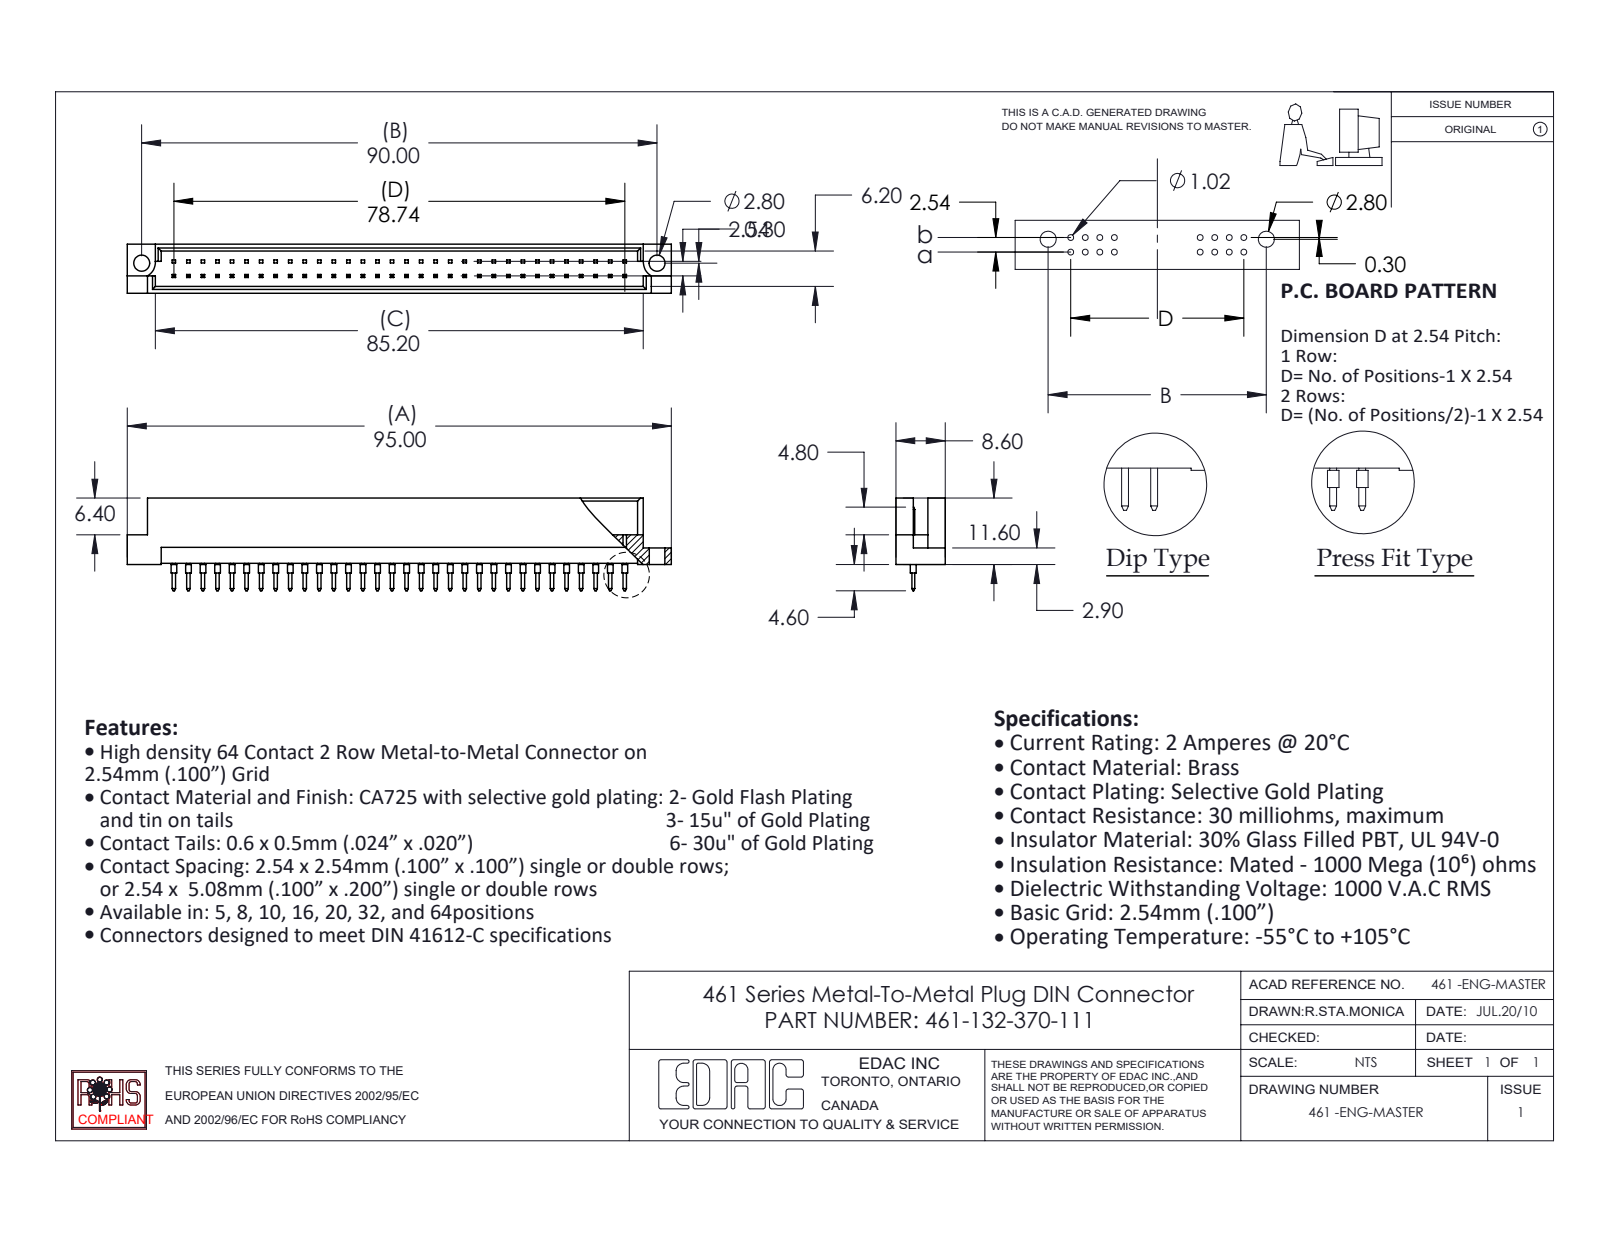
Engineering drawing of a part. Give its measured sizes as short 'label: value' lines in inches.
name: 461 Part_64; 461-132-370-111; 461-290_70
written by: SolidWorks 2020 (CONFIG_CONTROL_DESIGN)
unit: in
bodies: 33 solids, 1009 faces (938 planar, 71 cylindrical, 0 other)
size: 3.74 × 0.638 × 0.339
volume: 0.294 in³; area: 10.48 in²
holes: 2× ⌀0.11
bosses: 32× ⌀0.039
rounds: 2× R0.11
face distances: 0.047, 0.291, 0.339, 0.244, 0.197, 0.129, 0.209, 0.082, 0.162, 0.109
hole spacings: 3.543
